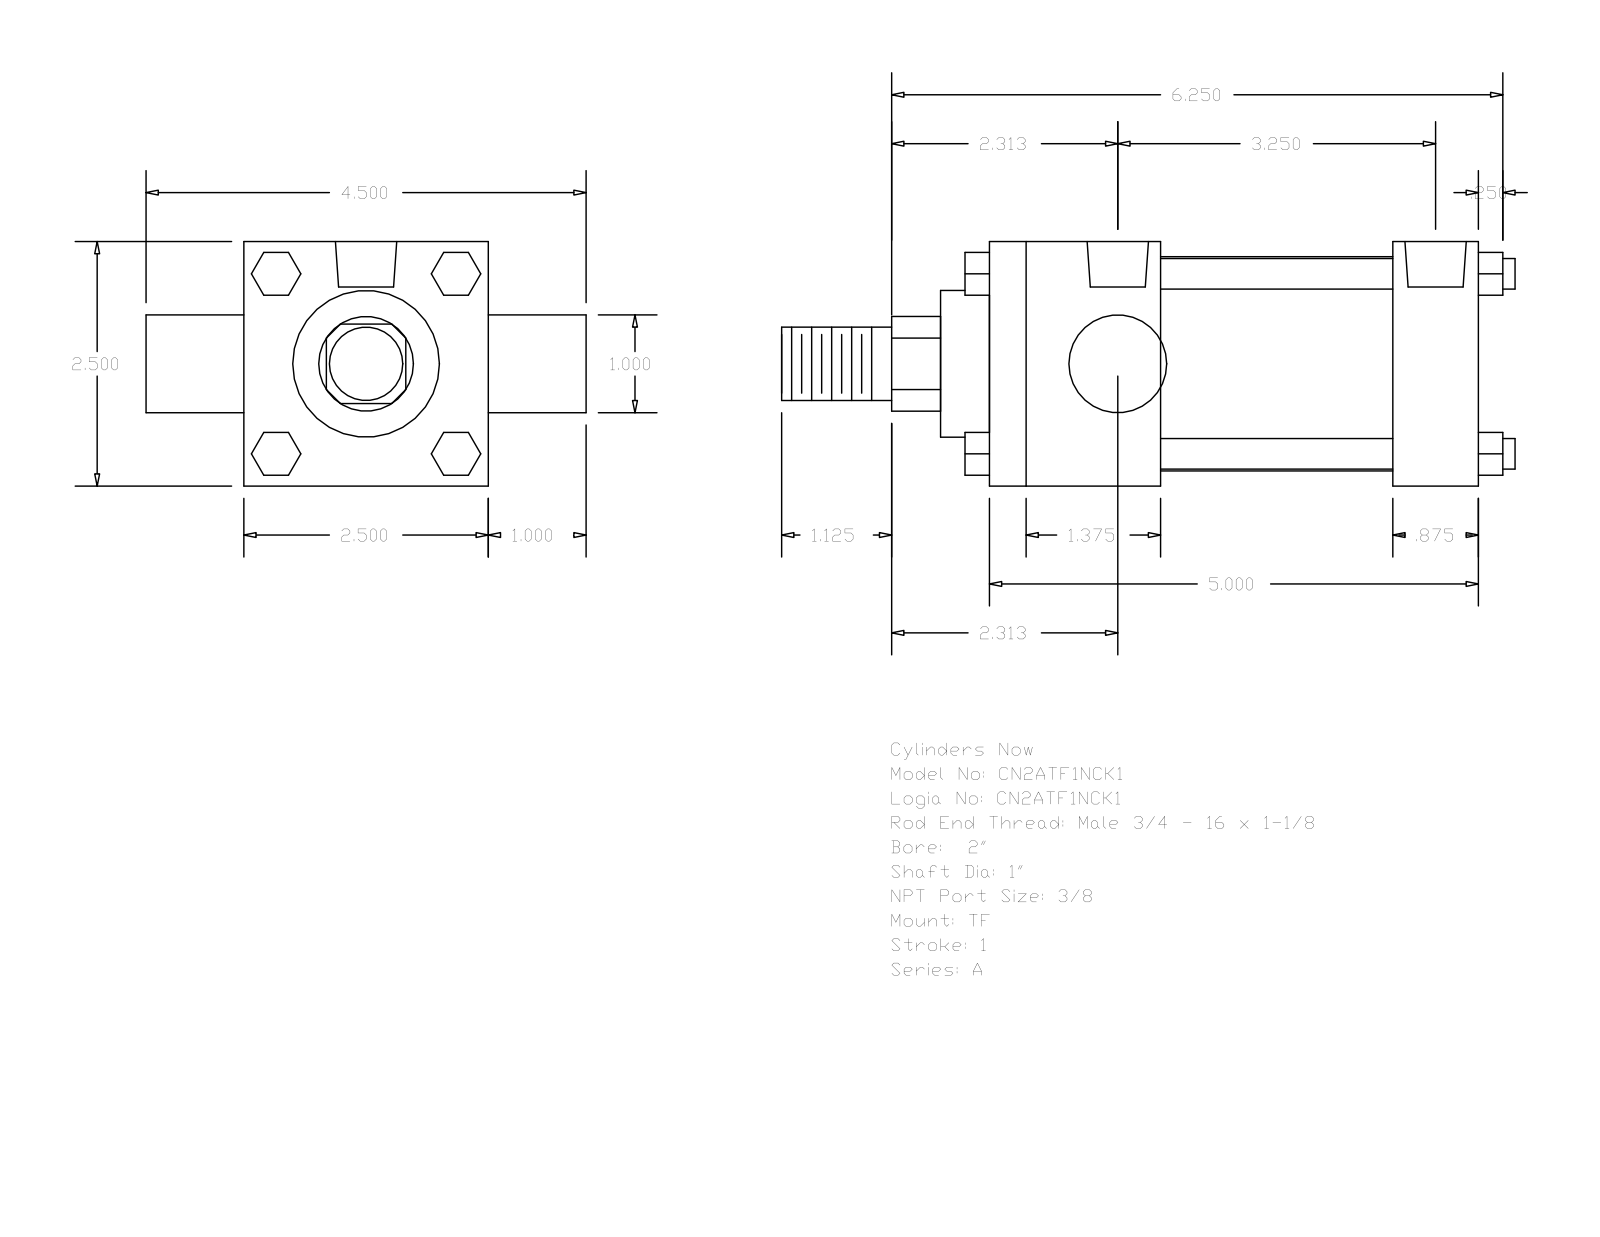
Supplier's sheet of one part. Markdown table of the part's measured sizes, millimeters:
| quantity | value |
| --- | --- |
| part name | A_TF__0200_1 |
| STEP written by | GSSL Pune (CONFIG_CONTROL_DESIGN) |
| units | millimeters |
| bodies | 0 solids, 120 faces (92 planar, 28 cylindrical, 0 other) |
| overall size | 190.5 × 114.3 × 63.5 |
| round holes (diameter × count) | 5.56 × 3, 15.93 × 2 |
| round bosses / shafts (diameter × count) | 7.94 × 4, 25.4 × 2, 55.63 × 1, 38.1 × 1, 19.05 × 1 |
| partial cylindrical surfaces (radius × count) | 12.29 × 1 |
| main face-to-face distances | 63.5, 127, 44.45, 104.78, 60.33, 82.55, 22.22, 88.9, 25.4, 139.7 |
| hole center spacings | 1.59, 3.98, 76.98, 78.57, 80.96, 82.55 |
